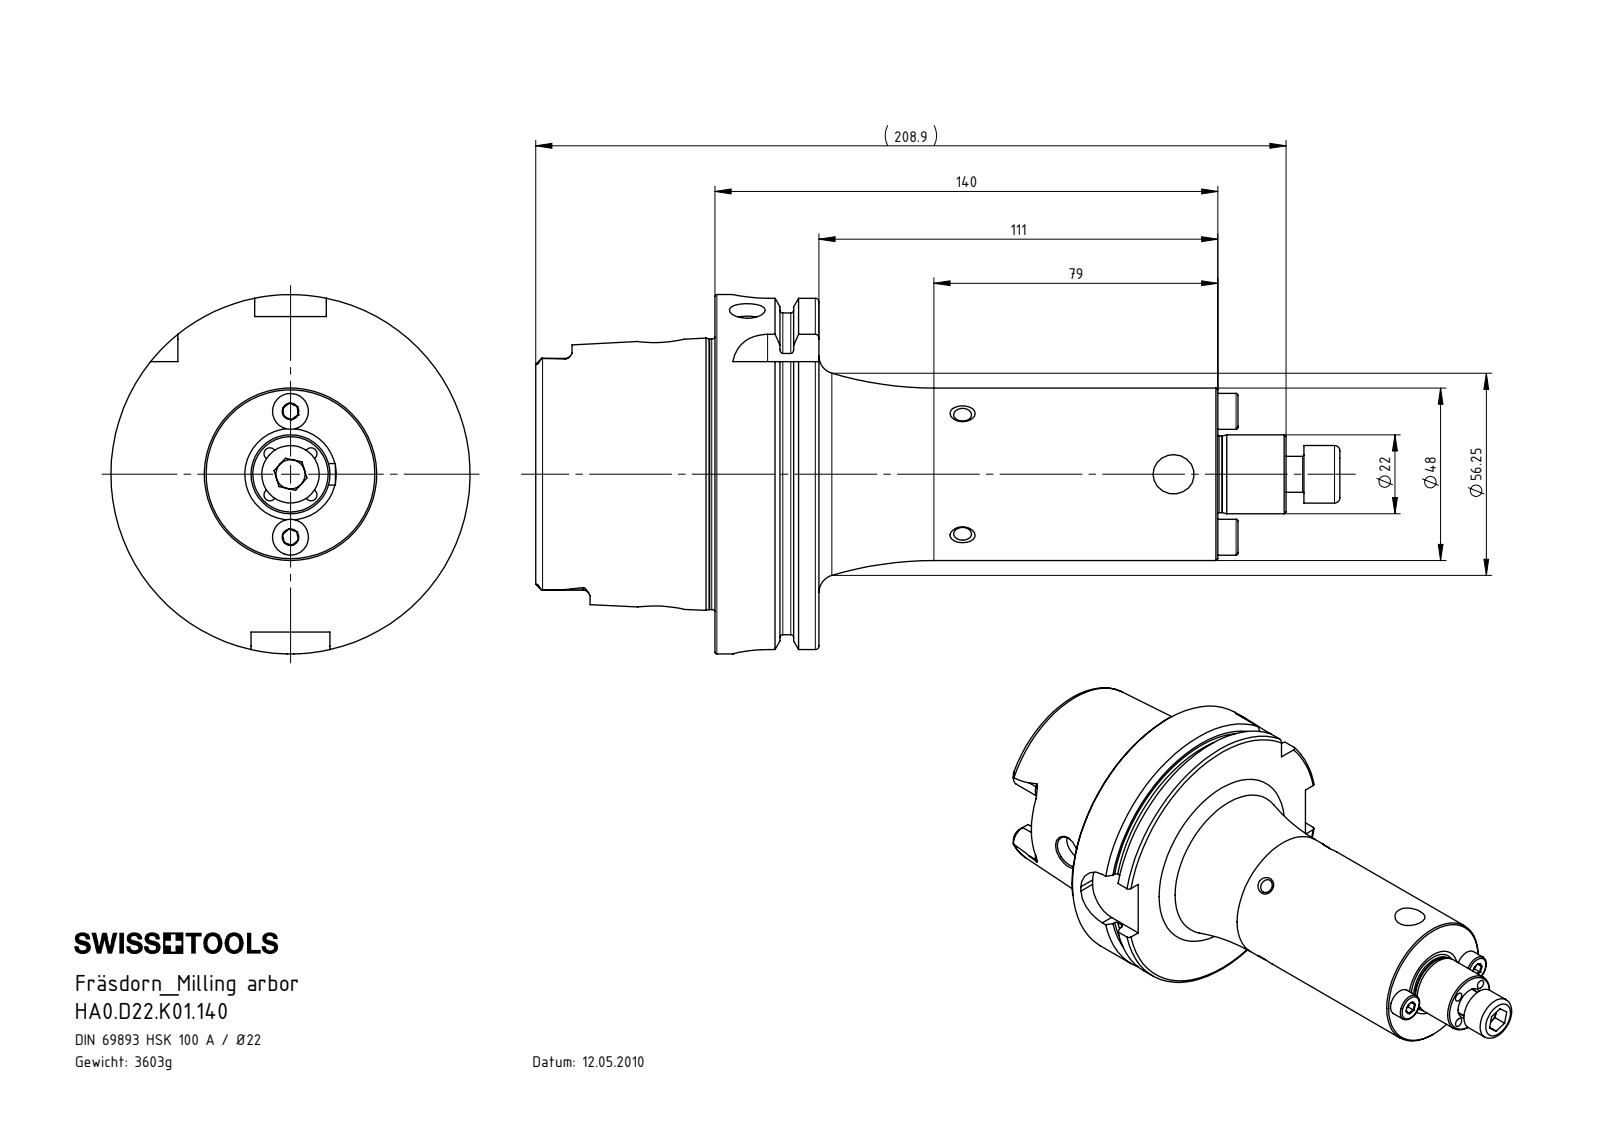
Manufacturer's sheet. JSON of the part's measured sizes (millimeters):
{"part_name": "HA0-D22.K01.140_B_Fertigbearbeitung; ISO 4762 - M10 x 25; HA0.D22.K01.140; D22-ER2.001.017_B (+1 more)", "step_written_by": "SolidWorks 2017 (AUTOMOTIVE_DESIGN)", "units": "millimeters", "bodies": {"solids": 5, "faces": 383, "planar": 89, "cylindrical": 119, "other": 175}, "overall_size": [223.9, 100, 100], "volume_mm3": 462136, "surface_area_mm2": 77457, "round_holes": [[3.3, 6], [5, 4], [10, 3], [4.2, 2], [8, 2], [12, 2], [8.5, 1], [10.5, 1], [22.5, 1], [26, 1], [53, 1], [63, 1]], "round_bosses_or_shafts": [[10, 3], [5, 2], [3.8, 2], [100, 1], [91.95, 1], [75.26, 1], [48, 1], [22, 1]], "partial_cylinders_radius": [[1.9, 6], [3, 4], [4.88, 4], [10, 4]], "face_to_face_distances": [28.95, 16.5, 12.45, 140, 127.55, 111.05, 49.9, 62.35, 78.85, 189.9], "hole_center_spacings": [8.13, 11.5, 13.08, 23.95, 62.05, 16.26, 17.5, 35]}
